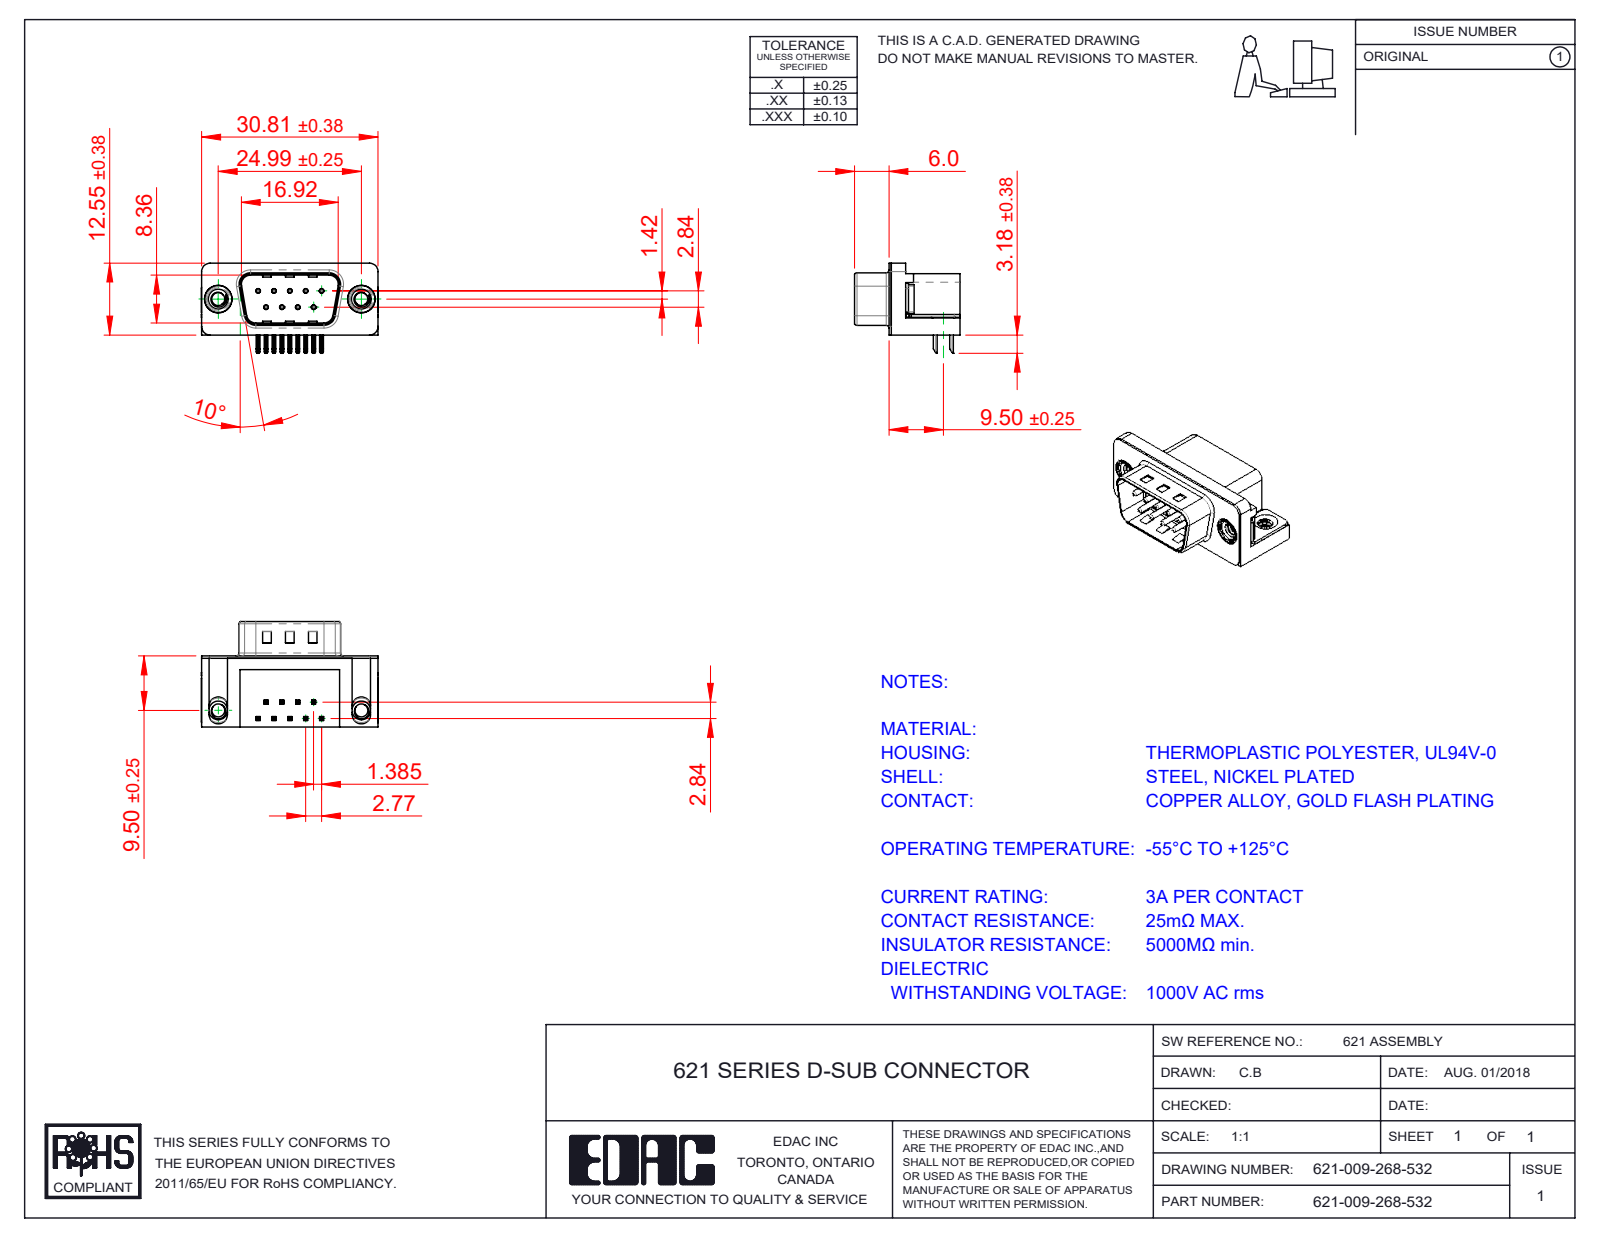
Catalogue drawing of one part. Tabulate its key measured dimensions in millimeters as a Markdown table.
| quantity | value |
| --- | --- |
| part name | 621-009-268-532; 621 Contact Top; 621 Shell_9 Socket; 621 Contact Bottom (+3 more) |
| STEP written by | SolidWorks 2016 (CONFIG_CONTROL_DESIGN) |
| units | millimeters |
| bodies | 15 solids, 1031 faces (605 planar, 323 cylindrical, 103 other) |
| overall size | 30.89 × 18.4 × 16.25 |
| volume | 3 246 mm³ |
| surface area | 4 427 mm² |
| round holes (diameter × count) | 0.35 × 9, 0.8 × 9, 2.26 × 2, 4 × 2, 4.8 × 2, 5 × 2 |
| round bosses / shafts (diameter × count) | 0.75 × 9, 4.9 × 2, 4.75 × 2, 3.9 × 2 |
| partial cylindrical surfaces (radius × count) | 0.25 × 44, 0.12 × 18, 1 × 16, 0.5 × 14, 1.5 × 8, 1.6 × 8, 0.32 × 4, 0.9 × 4 |
| main face-to-face distances | 0.4, 12, 12.4, 10.35, 0.5, 9.5, 2.5, 2.9, 2.1, 0.35 |
| hole center spacings | 3.16, 2.77, 5.54, 5.03, 5.04, 8.31, 7.48, 7.49 |
